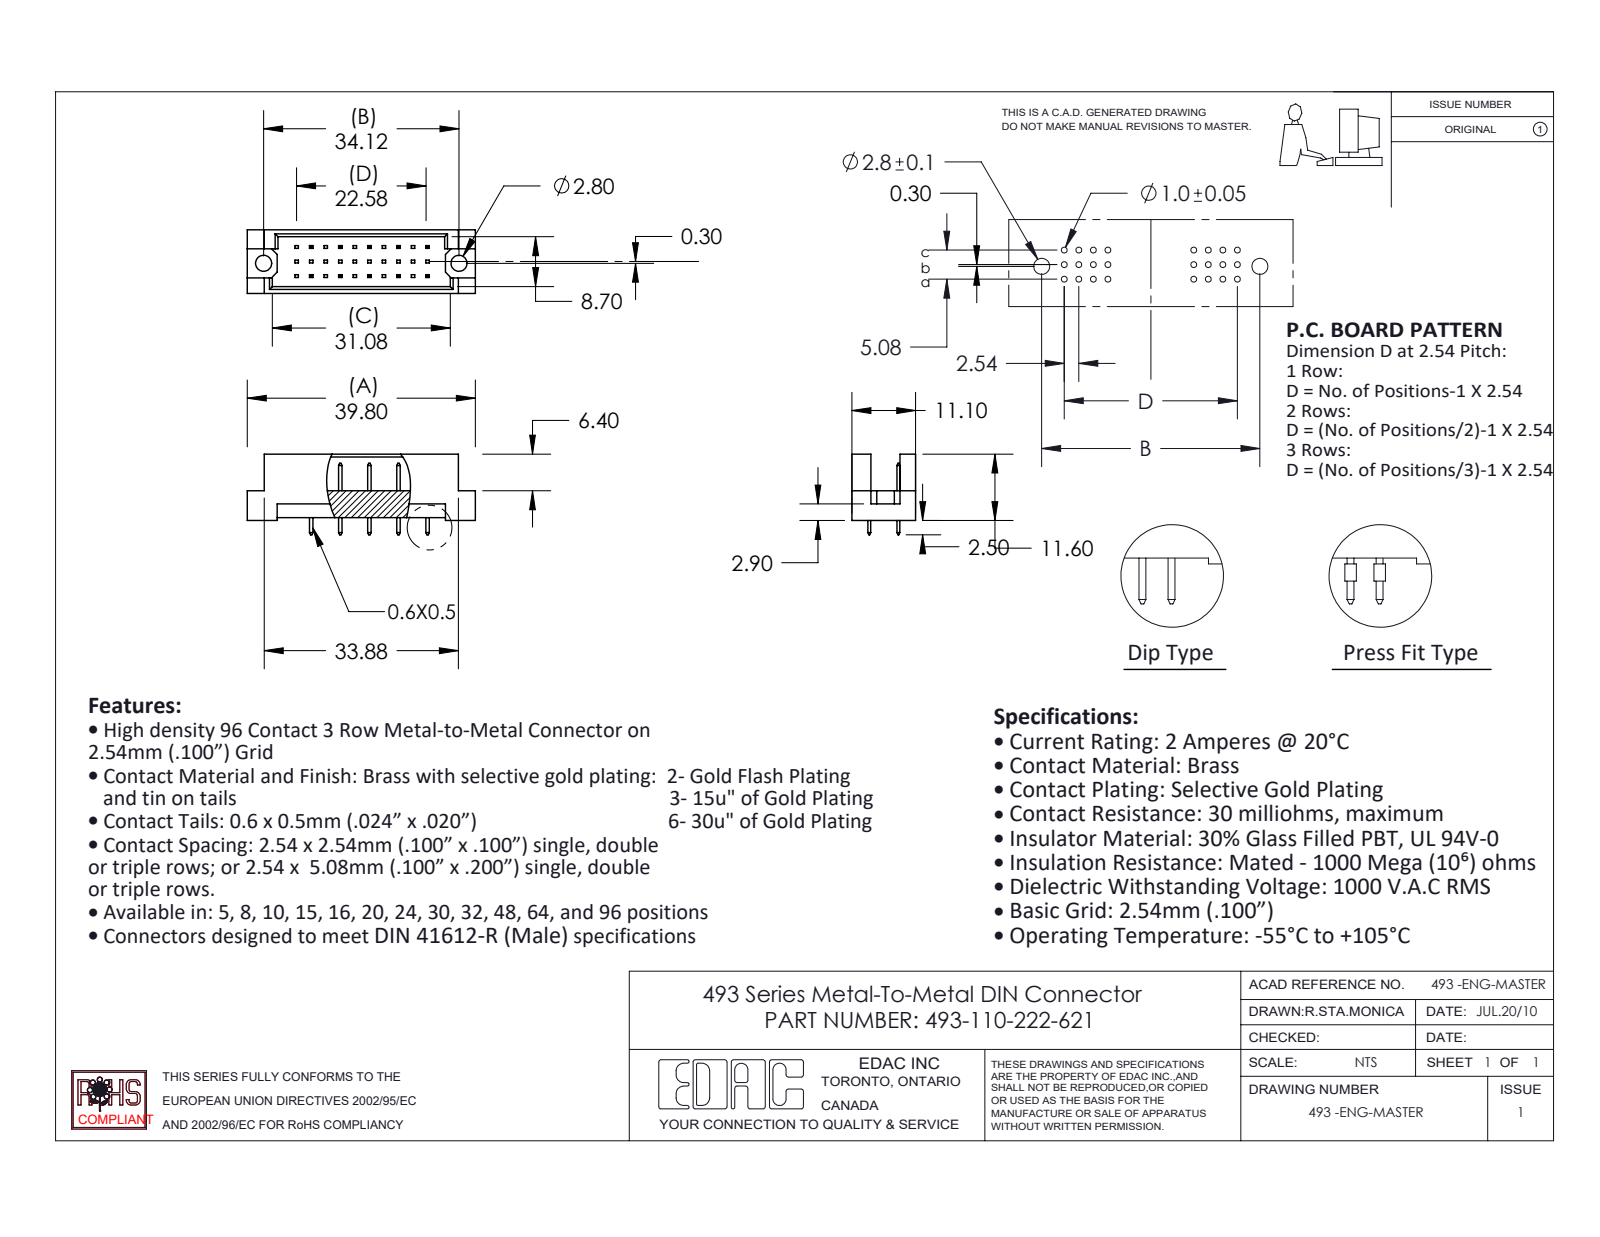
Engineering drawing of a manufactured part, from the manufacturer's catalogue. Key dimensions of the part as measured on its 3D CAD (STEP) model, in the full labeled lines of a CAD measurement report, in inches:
Part name (STEP PRODUCT): 493-110-222-622; 493 Part_30; 493-290_22
STEP written by: SolidWorks 2020 (CONFIG_CONTROL_DESIGN)
Units: inches
Bodies: 11 solids, 312 faces (308 planar, 4 cylindrical, 0 other)
Overall size (bounding box): 1.567 × 0.555 × 0.437
Volume: 0.147 in³ · Surface area: 4.664 in²
Round holes (diameter × count): ⌀0.11 ×2
Main face-to-face distances: 0.047, 0.39, 0.437, 0.2, 0.343, 0.02, 0.185, 0.094, 0.109, 0.128
Hole centre spacings: 1.343
